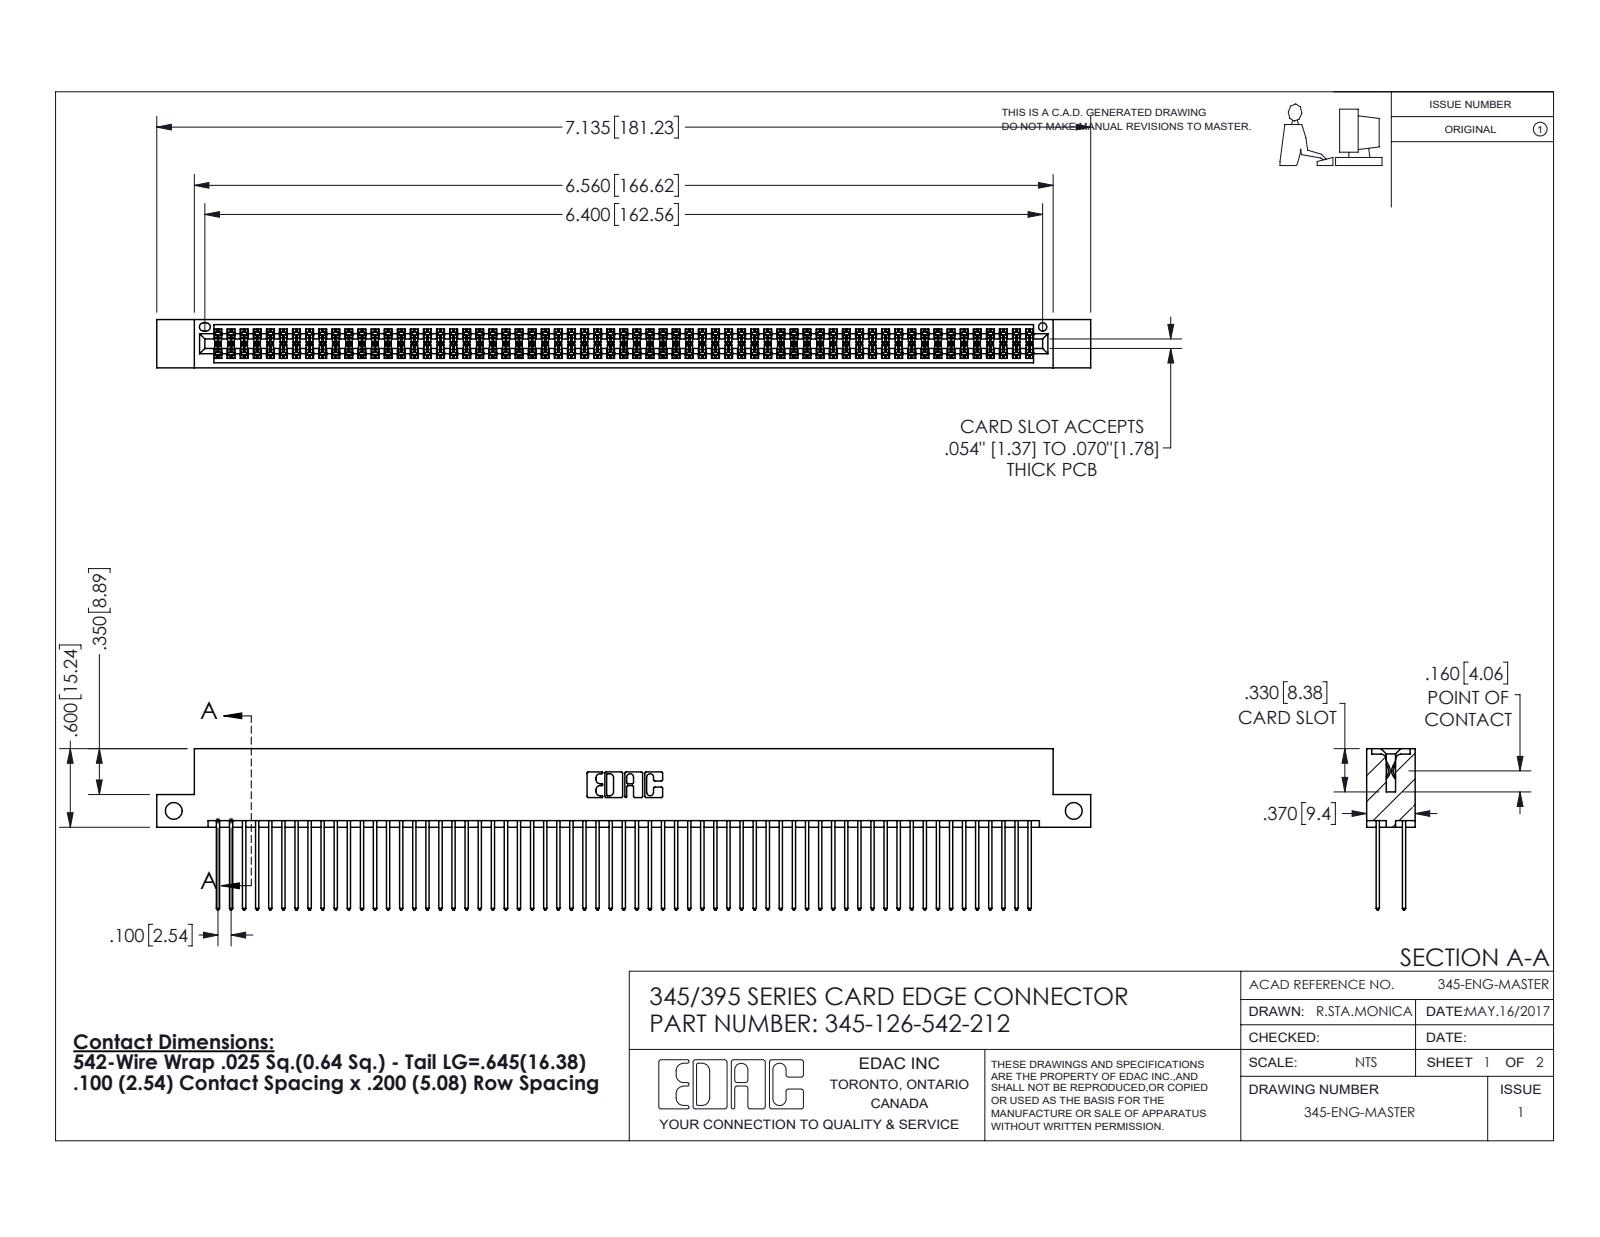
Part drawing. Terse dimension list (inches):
name: 345-126-542-212; 345 Part_Flush Mounting Lugs - Side Mount; 345-292-001_345-293-142
written by: SolidWorks 2016 (CONFIG_CONTROL_DESIGN)
unit: in
bodies: 127 solids, 6426 faces (4238 planar, 2188 cylindrical, 0 other)
size: 7.135 × 1.232 × 0.37
volume: 1.117 in³; area: 46.6 in²
holes: 2× ⌀0.128, 1× ⌀0.064
rounds: 189× R0.006, 126× R0.01, 22× R0.01, 6× R0.007, 6× R0.031, 3× R0.026, 2× R0.014, 2× R0.019
face distances: 0.298, 0.072, 0.2, 0.098, 0.272, 0.025, 0.225, 0.37, 0.175, 0.149
hole spacings: 6.875
